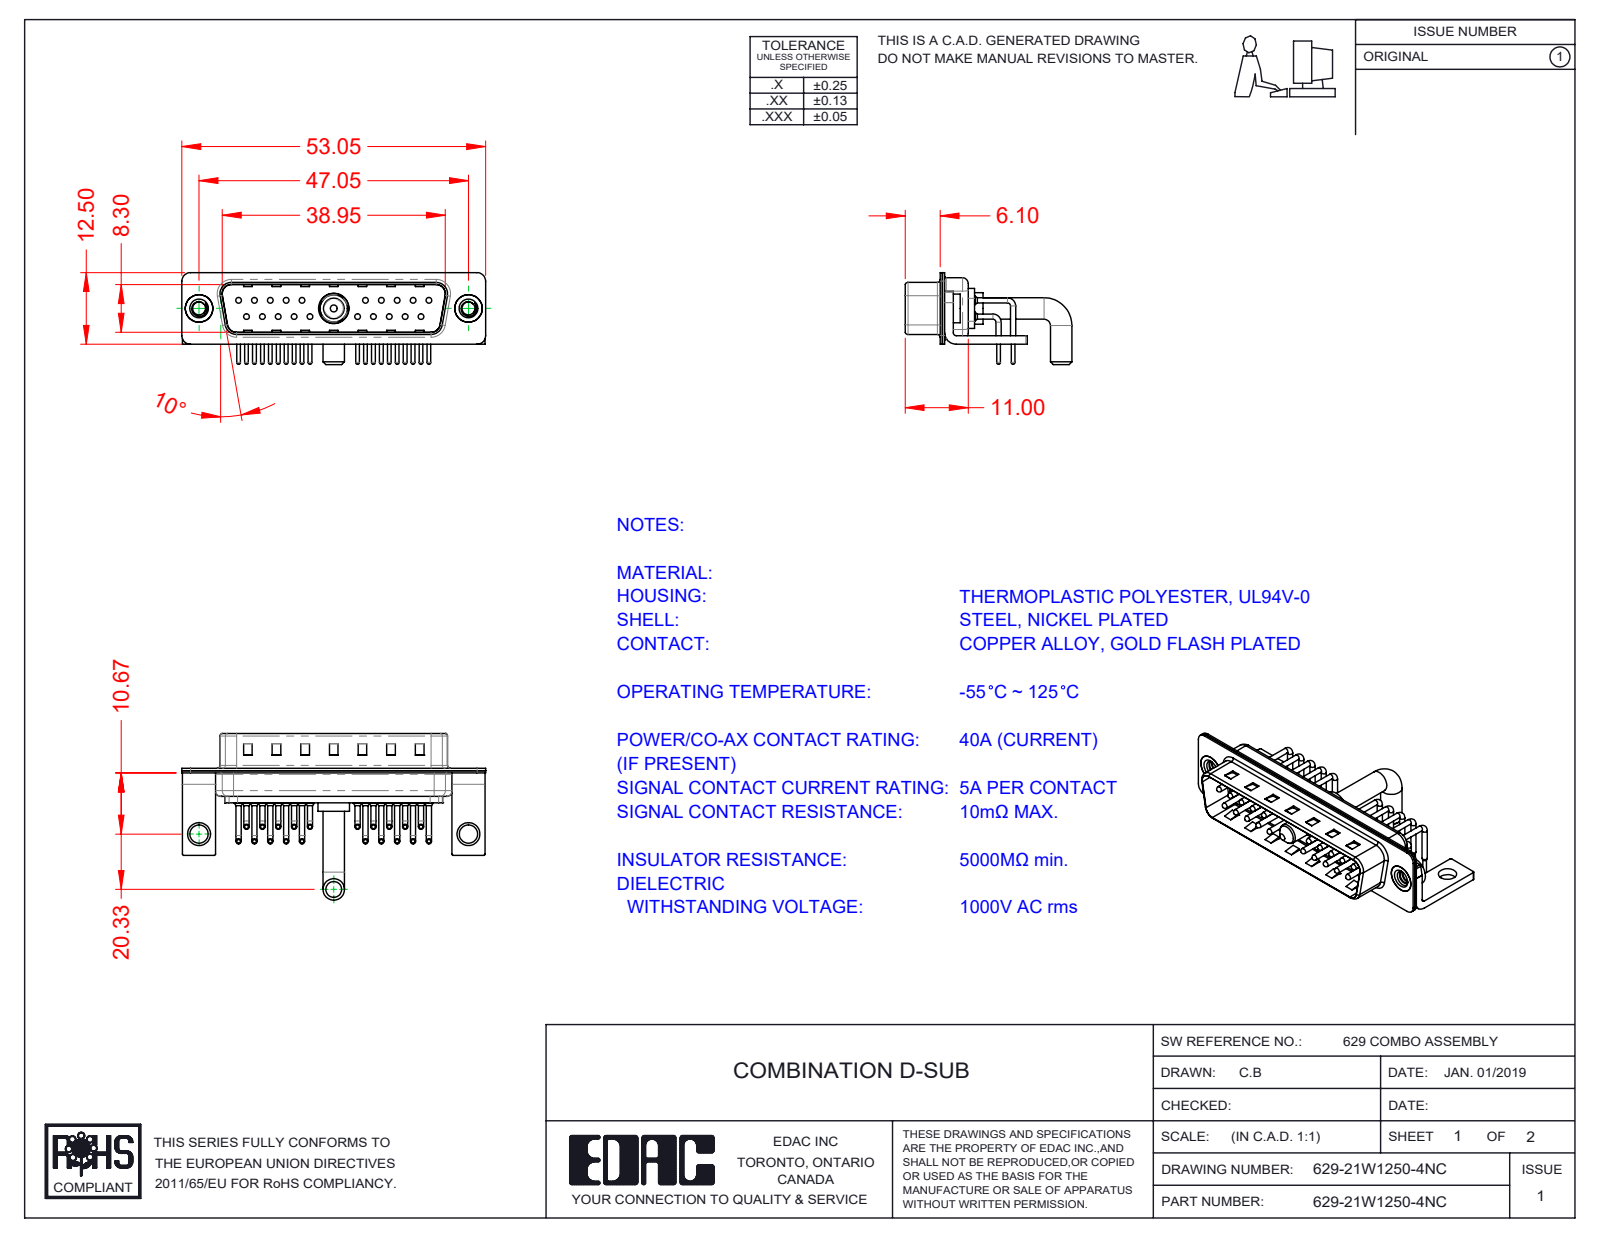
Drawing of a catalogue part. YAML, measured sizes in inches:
part_name: "629-21W1250-4NC; 629Combo Threaded Rivet_2; 629Combo Housing_21W1; 629Combo Shell Front_25 Contacts (+5 more)"
step_written_by: "SolidWorks 2020 (CONFIG_CONTROL_DESIGN)"
units: inches
bodies: {solids: 29, faces: 2667, planar: 1481, cylindrical: 902, other: 284}
overall_size: [2.089, 1.146, 0.632]
volume: 0.212
surface_area: 12.97
round_holes:
  - {diameter: 0.03, count: 20}
  - {diameter: 0.063, count: 20}
  - {diameter: 0.079, count: 20}
  - {diameter: 0.089, count: 2}
  - {diameter: 0.126, count: 2}
  - {diameter: 0.157, count: 2}
  - {diameter: 0.189, count: 2}
  - {diameter: 0.191, count: 1}
  - {diameter: 0.209, count: 1}
round_bosses_or_shafts:
  - {diameter: 0.035, count: 40}
  - {diameter: 0.059, count: 20}
  - {diameter: 0.039, count: 20}
  - {diameter: 0.026, count: 20}
  - {diameter: 0.197, count: 2}
  - {diameter: 0.193, count: 2}
  - {diameter: 0.148, count: 2}
  - {diameter: 0.217, count: 1}
partial_cylinders:
  - {radius: 0.04, count: 20}
  - {radius: 0.01, count: 16}
  - {radius: 0.059, count: 16}
  - {radius: 0.079, count: 13}
  - {radius: 0.02, count: 9}
  - {radius: 0.063, count: 8}
  - {radius: 0.024, count: 4}
  - {radius: 0.026, count: 4}
face_to_face_distances: [0.016, 0.031, 0.374, 0.059, 0.358, 0.343, 0.39, 0.024, 0.047, 0.083]
hole_center_spacings: [0.124, 0.109, 0.218, 0.327, 0.198, 0.763, 0.826, 0.872]
